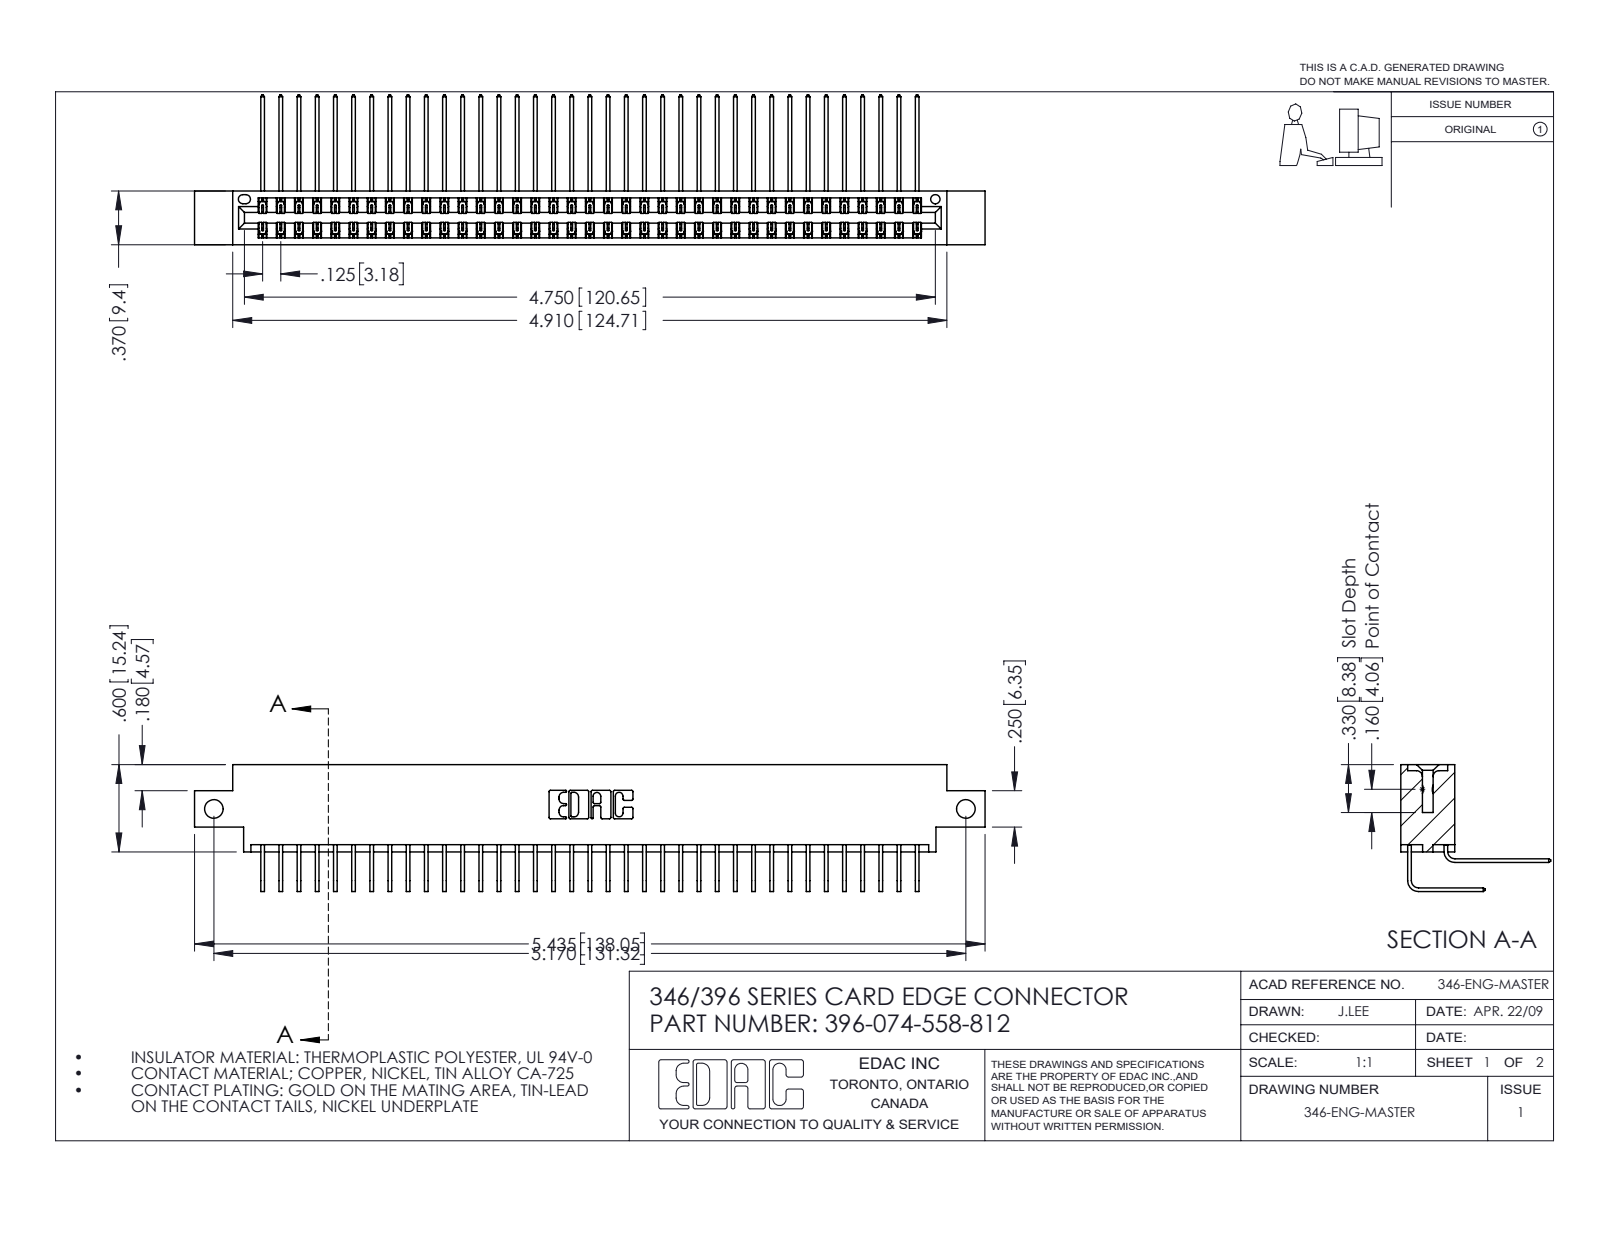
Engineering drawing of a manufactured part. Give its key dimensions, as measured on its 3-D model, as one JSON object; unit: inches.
{"part_name": "396-074-558-812; 345-292-001_558 Tail - 2; 345-292-001_558 559 Tail - 1; 346 Part_0.170 Offset - Side Mount", "step_written_by": "SolidWorks 2016 (CONFIG_CONTROL_DESIGN)", "units": "inches", "bodies": {"solids": 75, "faces": 4122, "planar": 2818, "cylindrical": 1304, "other": 0}, "overall_size": [5.435, 1.03, 0.873], "volume_in3": 0.83, "surface_area_in2": 32.11, "round_holes": [[0.128, 2], [0.064, 1]], "partial_cylinders_radius": [[0.006, 111], [0.01, 22], [0.007, 6], [0.031, 6], [0.026, 3], [0.014, 2], [0.022, 2], [0.024, 2]], "face_to_face_distances": [0.322, 0.048, 0.025, 0.37, 0.25, 0.298, 0.072, 0.275, 0.148, 0.222], "hole_center_spacings": [5.17]}
